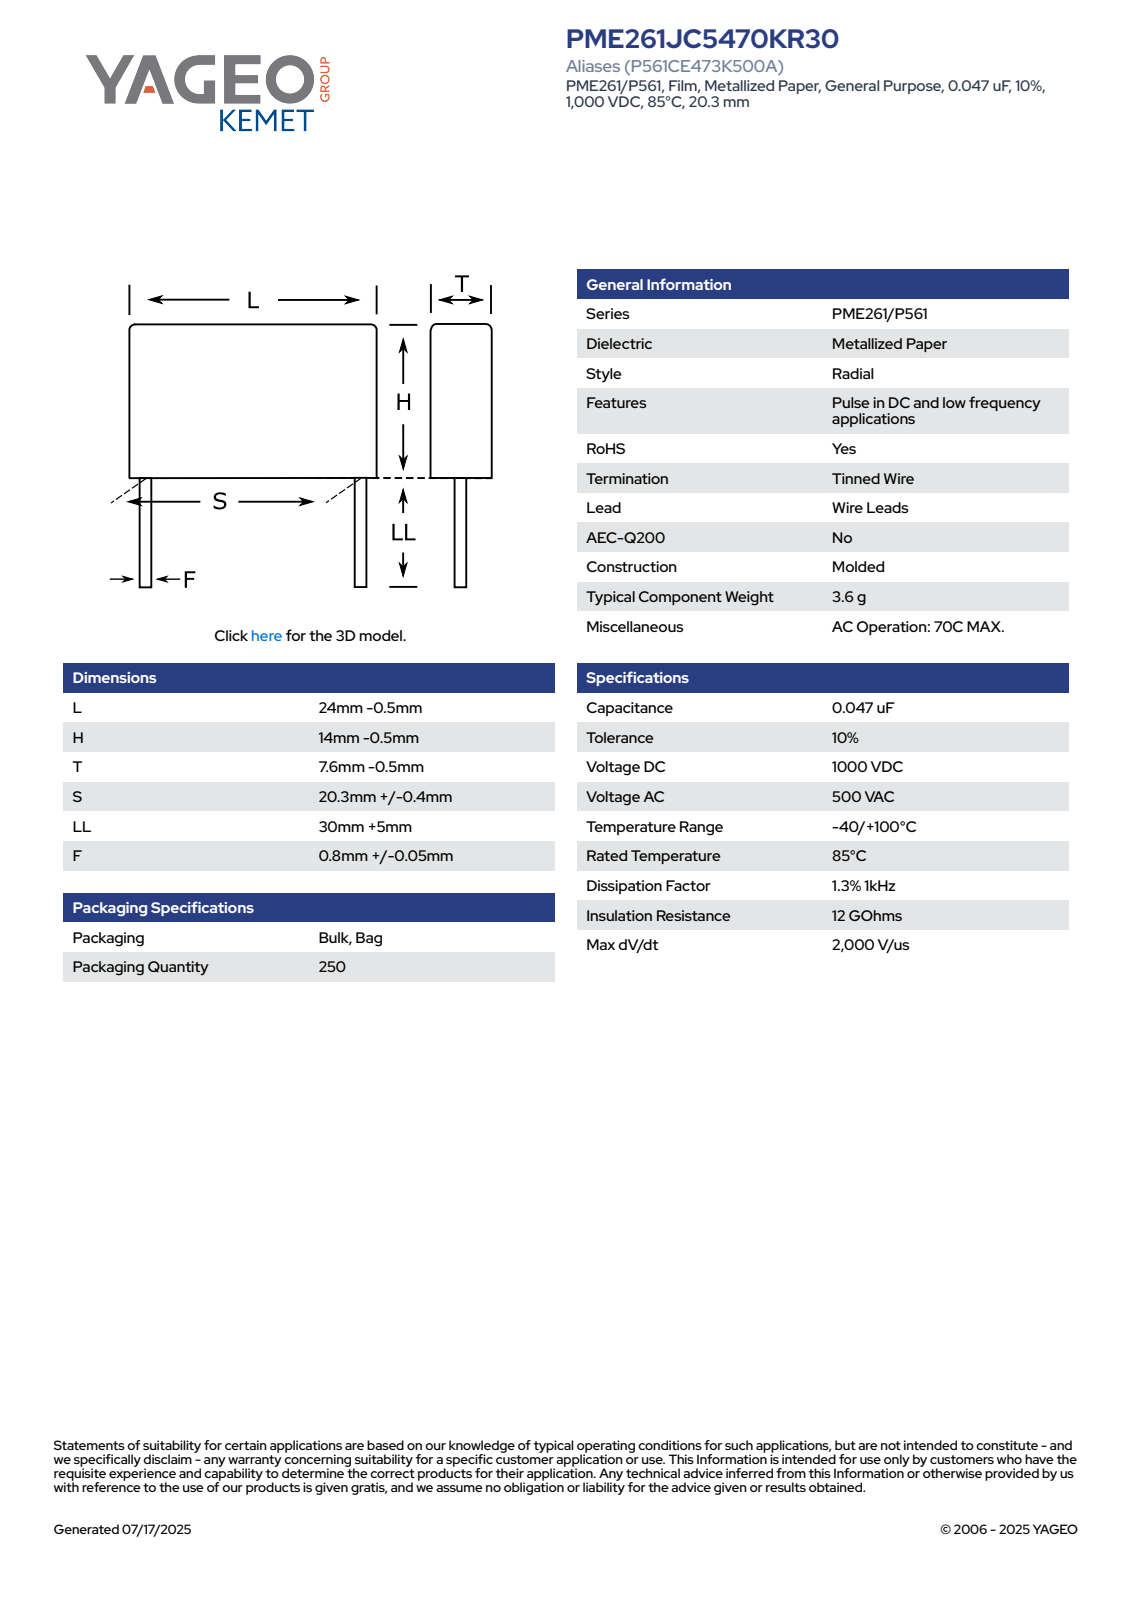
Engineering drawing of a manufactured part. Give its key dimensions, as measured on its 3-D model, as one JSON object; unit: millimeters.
{"part_name": "CFR_MOLDED_24X14X7.6_L23.5H13.5T7.1S20.3LL35F0.85", "step_written_by": "SolidWorks 2014 (AUTOMOTIVE_DESIGN)", "units": "millimeters", "bodies": {"solids": 4, "faces": 73, "planar": 65, "cylindrical": 8, "other": 0}, "overall_size": [48.5, 23.5, 7.11], "volume_mm3": 2289, "surface_area_mm2": 1360, "round_bosses_or_shafts": [[0.85, 2]], "partial_cylinders_radius": [[0.5, 4]], "face_to_face_distances": [7.1, 13.5, 23.5, 35, 48.5, 42.77, 7.77, 5.73, 40.66, 5.66]}
